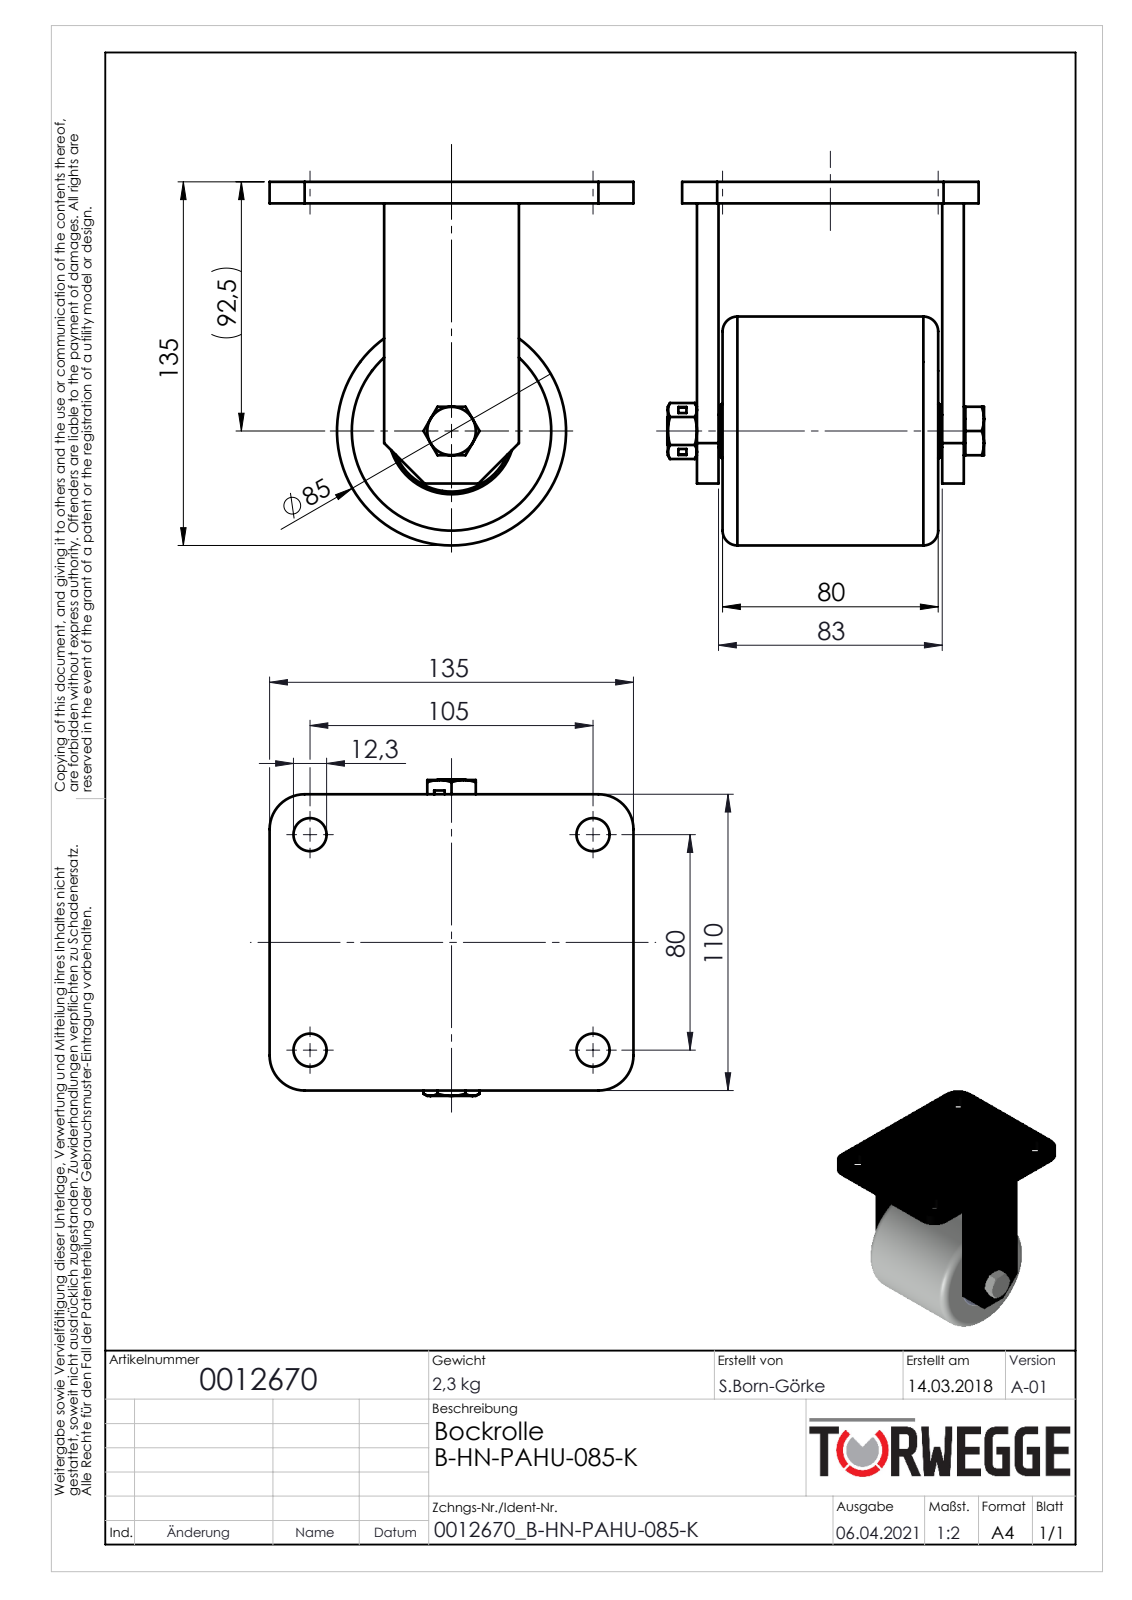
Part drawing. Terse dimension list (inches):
name: 0012670
written by: SolidWorks 2020 (AUTOMOTIVE_DESIGN)
unit: in
bodies: 0 solids, 168 faces (70 planar, 48 cylindrical, 50 other)
size: 5.315 × 5.315 × 4.626
holes: 4× ⌀0.484, 1× ⌀0.402, 1× ⌀0.472, 1× ⌀0.488, 1× ⌀0.492, 1× ⌀0.787, 1× ⌀1.531, 1× ⌀1.575, 1× ⌀1.85
bosses: 1× ⌀3.346, 1× ⌀1.106, 1× ⌀0.709
rounds: 4× R0.512
face distances: 0.315, 3.583, 0.374, 3.524, 0.059, 3.209, 3.898, 3.268, 3.15, 3.799
hole spacings: 3.15, 4.134, 5.197
